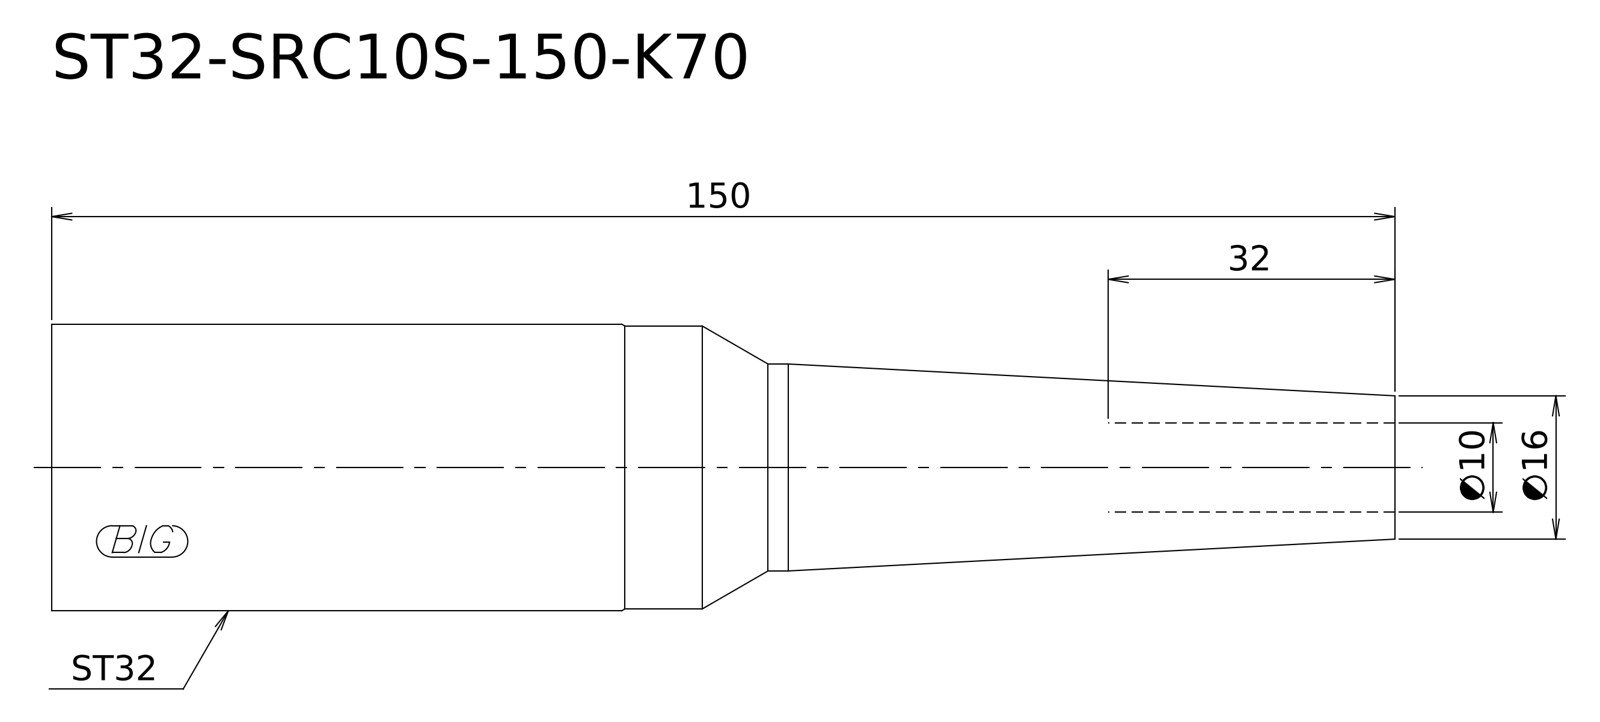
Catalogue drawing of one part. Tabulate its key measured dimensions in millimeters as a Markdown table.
| quantity | value |
| --- | --- |
| STEP written by | Kubotek KeyCreator V8.5.1 (14335) (CONFIG_CONTROL_DESIGN) |
| units | millimeters |
| bodies | 1 solid, 8 faces (2 planar, 3 cylindrical, 3 other) |
| overall size | 150 × 32 × 32 |
| volume | 84 098 mm³ |
| surface area | 13 362 mm² |
| round bosses / shafts (diameter × count) | 32 × 1, 31.6 × 1, 23.1 × 1 |
| main face-to-face distances | 150 |
